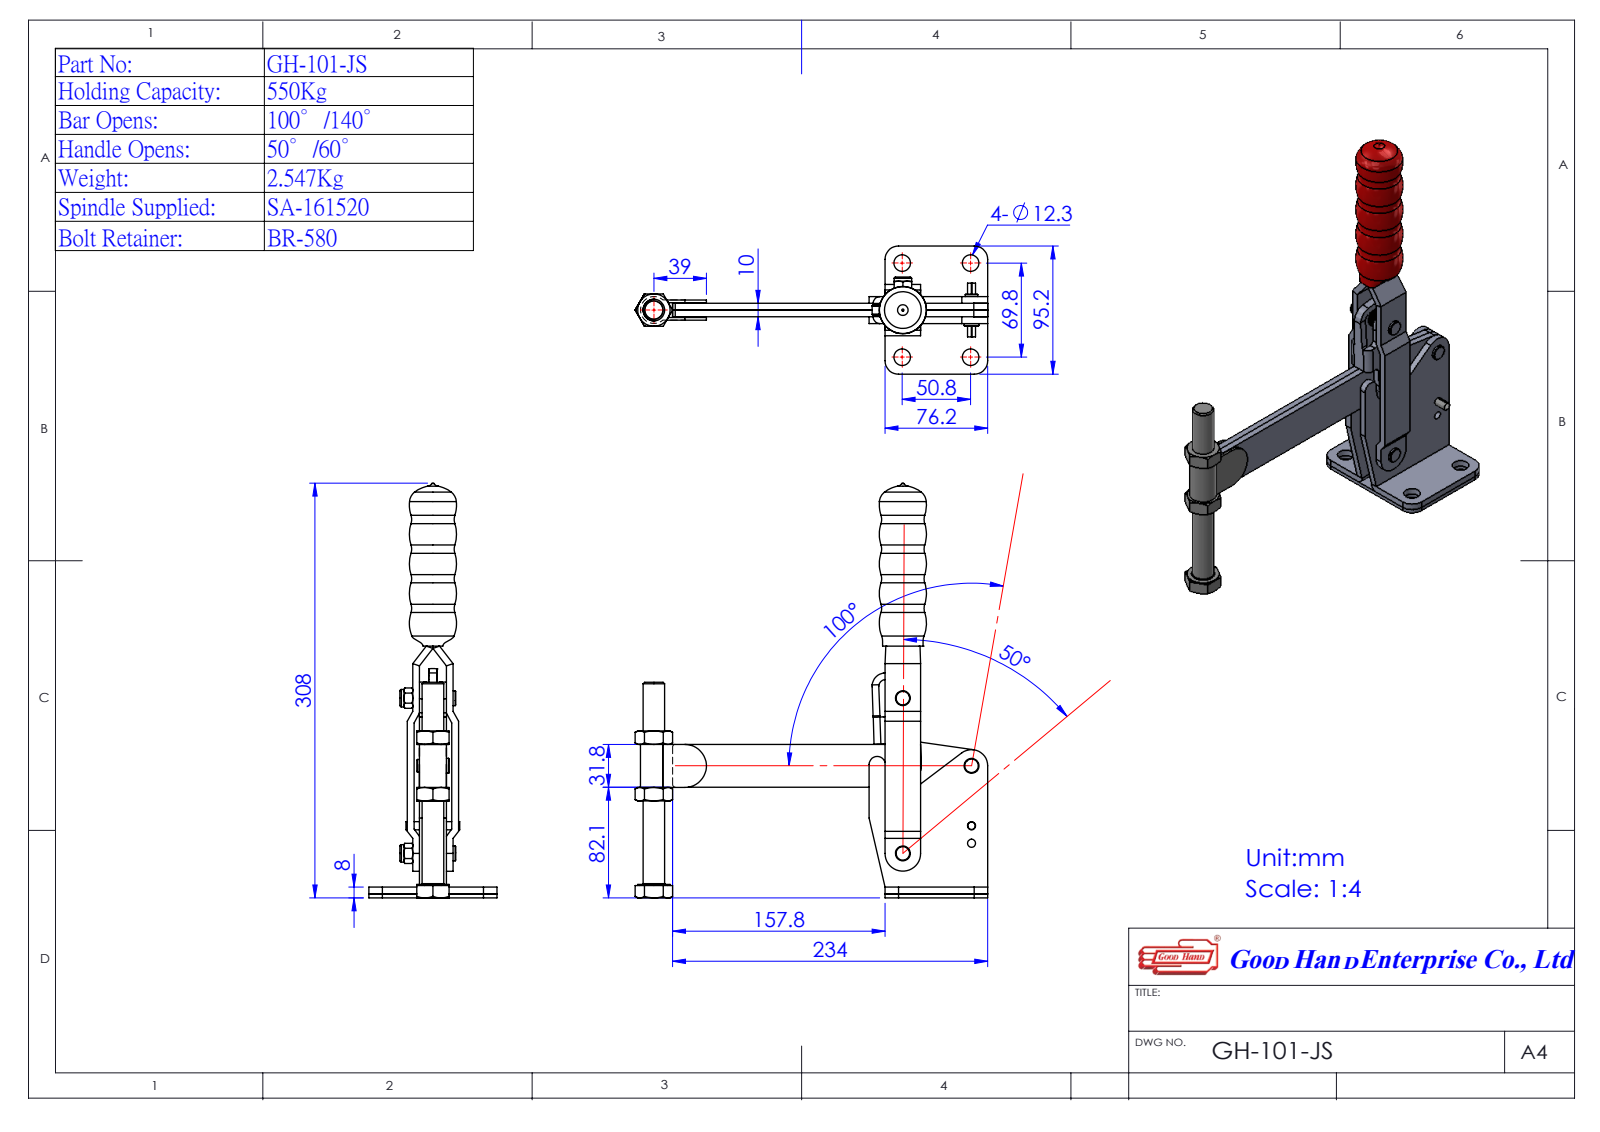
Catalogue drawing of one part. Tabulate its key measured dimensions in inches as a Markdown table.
| quantity | value |
| --- | --- |
| part name | GH-101-JS(簡化)-1; Group1^GH-101-JS(簡化)-1; Group6^GH-101-JS(簡化)-1; Group2^GH-101-JS(簡化)-1 (+2 more) |
| STEP written by | SolidWorks 2016 (AUTOMOTIVE_DESIGN) |
| units | inches |
| bodies | 4 solids, 345 faces (146 planar, 119 cylindrical, 80 other) |
| overall size | 12.118 × 10.926 × 3.748 |
| volume | 16.3 in³ |
| surface area | 208.3 in² |
| round holes (diameter × count) | 0.236 × 5, 0.484 × 4, 0.217 × 1 |
| round bosses / shafts (diameter × count) | 0.433 × 4, 0.315 × 2, 0.313 × 2, 0.945 × 1, 0.63 × 1, 0.236 × 1 |
| partial cylindrical surfaces (radius × count) | 0.039 × 4, 0.197 × 4, 0.394 × 4, 0.472 × 3, 0.079 × 2, 0.118 × 2, 0.433 × 2, 0.236 × 1 |
| main face-to-face distances | 0.197, 0.591, 0.394, 0.787, 0.945, 0.354, 0.157, 1.142, 0.315, 0.118 |
| hole center spacings | 2, 2.748, 3.399, 0.512, 1.751, 1.939, 1.978, 2.03 |
